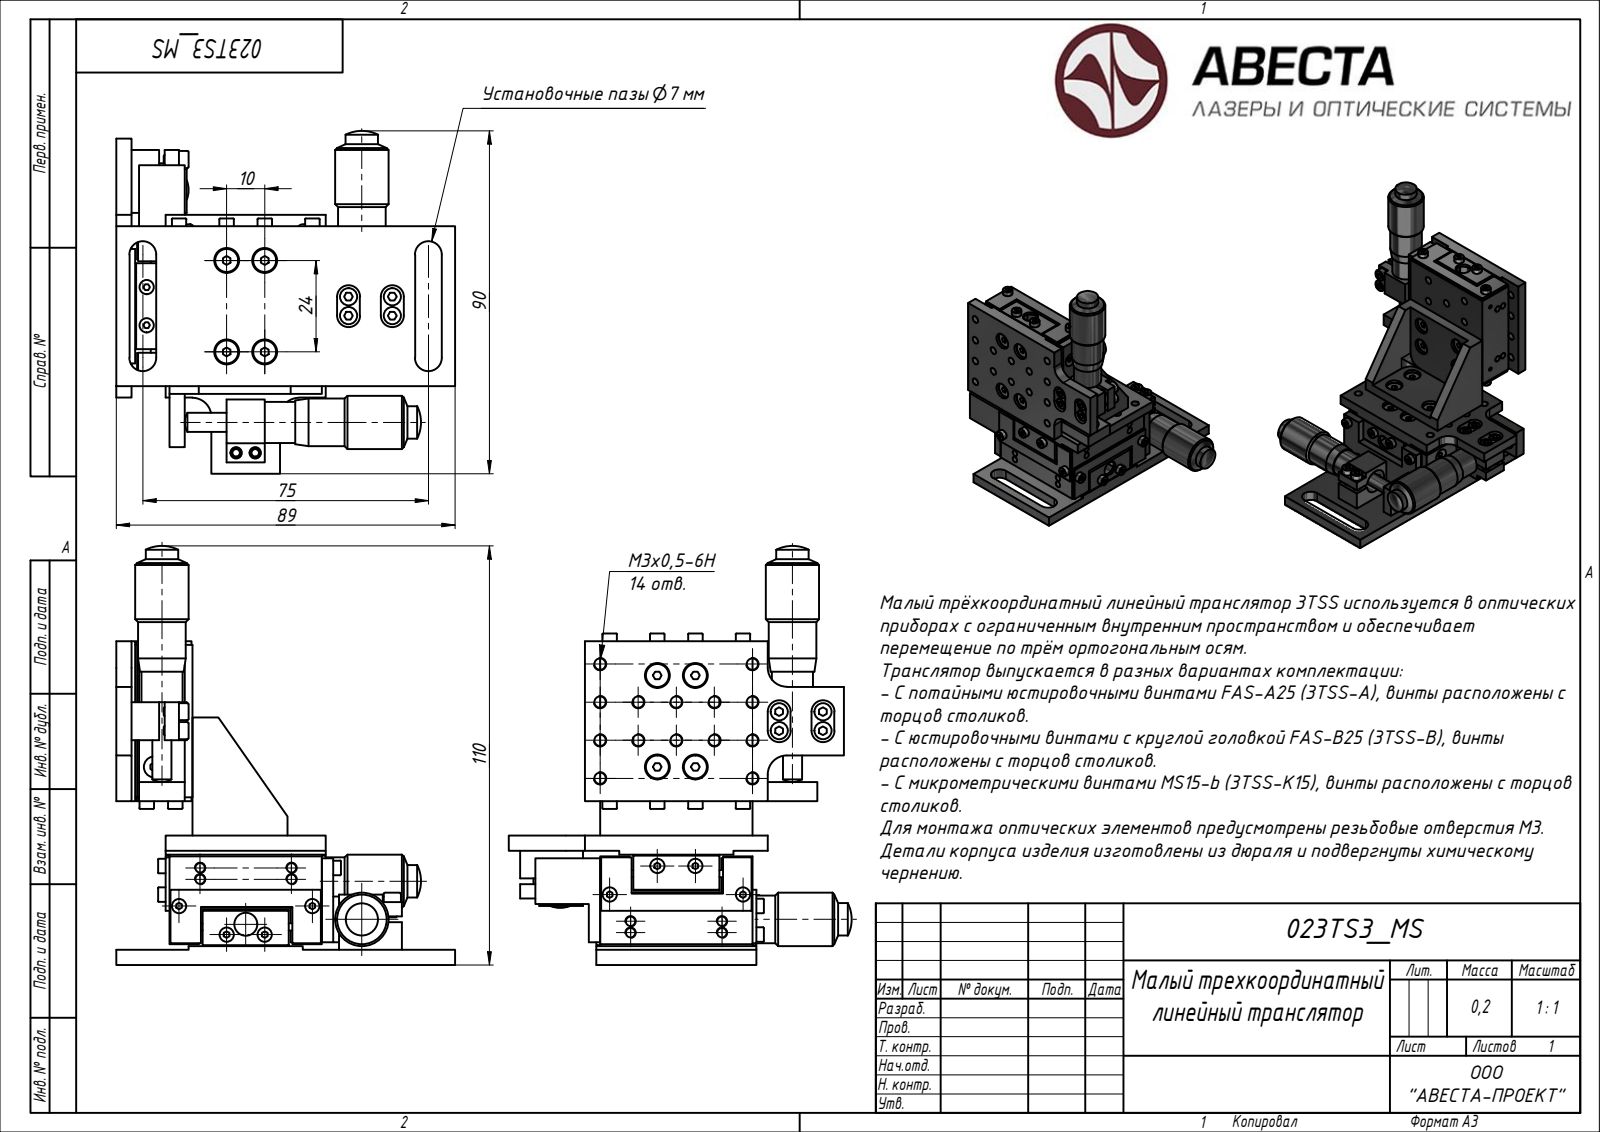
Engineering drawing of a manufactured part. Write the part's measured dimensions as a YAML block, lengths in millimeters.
part_name: "Block 01"
step_written_by: "ST-DEVELOPER v15 (AUTOMOTIVE_DESIGN)"
units: millimeters
bodies: {solids: 25, faces: 1583, planar: 0, cylindrical: 0, other: 1583}
overall_size: [110, 90, 89]
